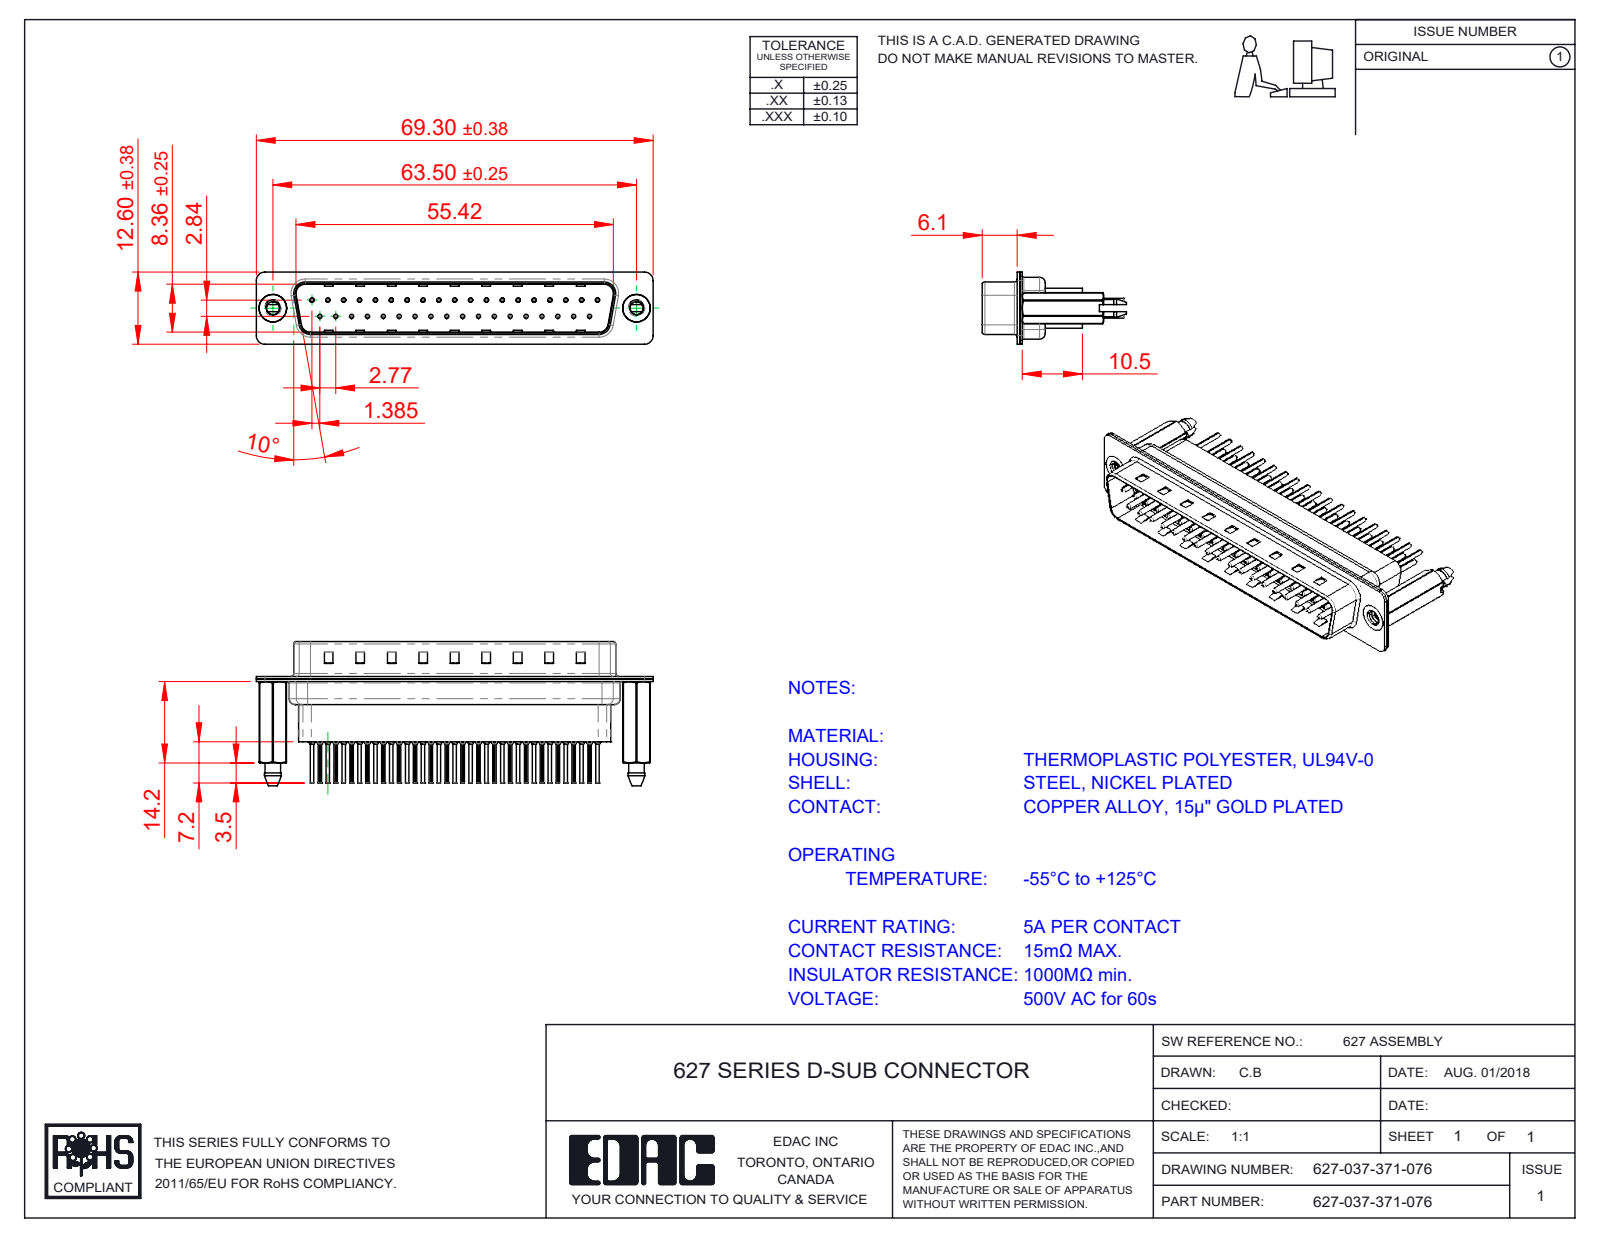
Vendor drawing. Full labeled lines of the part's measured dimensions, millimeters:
Part name (STEP PRODUCT): 627 Shell Rear_37 Contacts; 627 Contact Row 2_61; 627 Contact Row 1_61; 627-037-371-076 (+3 more)
STEP written by: SolidWorks 2020 (CONFIG_CONTROL_DESIGN)
Units: millimetres
Bodies: 42 solids, 4146 faces (1123 planar, 1576 cylindrical, 1447 other)
Overall size (bounding box): 69.3 × 25.1 × 12.6
Volume: 5 699 mm³ · Surface area: 14 707 mm²
Round holes (diameter × count): ⌀0.2 ×37, ⌀0.35 ×37, ⌀1.1 ×37, ⌀1.6 ×37, ⌀2.26 ×2, ⌀4 ×2, ⌀4.8 ×2
Round bosses / shafts (diameter × count): ⌀2 ×37, ⌀1.5 ×37, ⌀0.75 ×37, ⌀0.6 ×37, ⌀4.9 ×2
Partial cylindrical surfaces — rounded edges, fillets, slot ends (radius × count): R0.1 ×74, R1.5 ×18, R2 ×12, R1.6 ×10, R0.5 ×8, R0.25 ×4, R0.6 ×4, R0.65 ×4
Main face-to-face distances: 0.4, 0.82, 9.58, 0.68, 7.68, 0.45, 1.5, 1.08, 8.08, 8.76
Hole centre spacings: 3.16, 2.77, 5.54, 8.31, 5.04, 10.1, 11.08, 12.78
